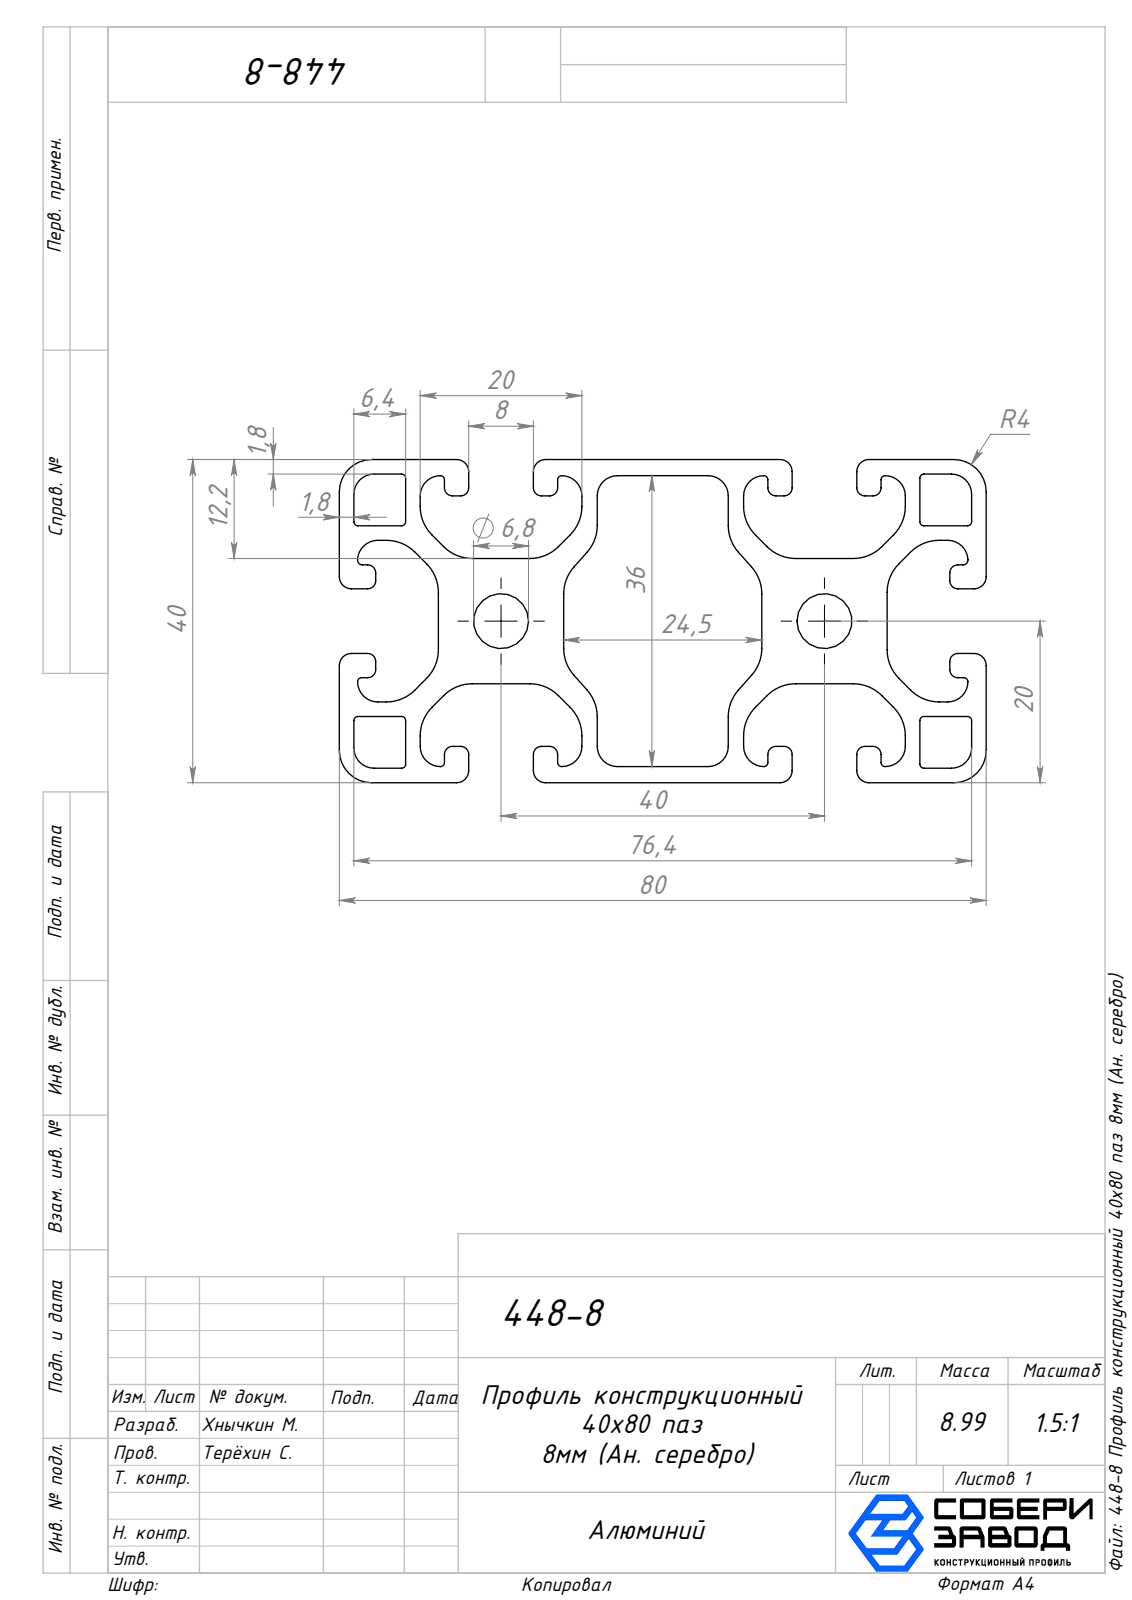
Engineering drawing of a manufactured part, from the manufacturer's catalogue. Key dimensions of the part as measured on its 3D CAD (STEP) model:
Part name (STEP PRODUCT): V053-8944
STEP written by: SolidWorks 2025 (AUTOMOTIVE_DESIGN)
Units: millimetres
Bodies: 1 solid, 222 faces (106 planar, 116 cylindrical, 0 other)
Overall size (bounding box): 1000 × 80 × 40
Volume: 1 156 000 mm³ · Surface area: 762 910 mm²
Round holes (diameter × count): ⌀6.8 ×2
Partial cylindrical surfaces — rounded edges, fillets, slot ends (radius × count): R5 ×32, R0.5 ×24, R1 ×24, R2.5 ×16, R1.5 ×12, R4 ×4
Main face-to-face distances: 40, 8.2, 27.75, 19.55, 31.8, 4.05, 1.8, 80, 12.25, 30
Hole centre spacings: 40
